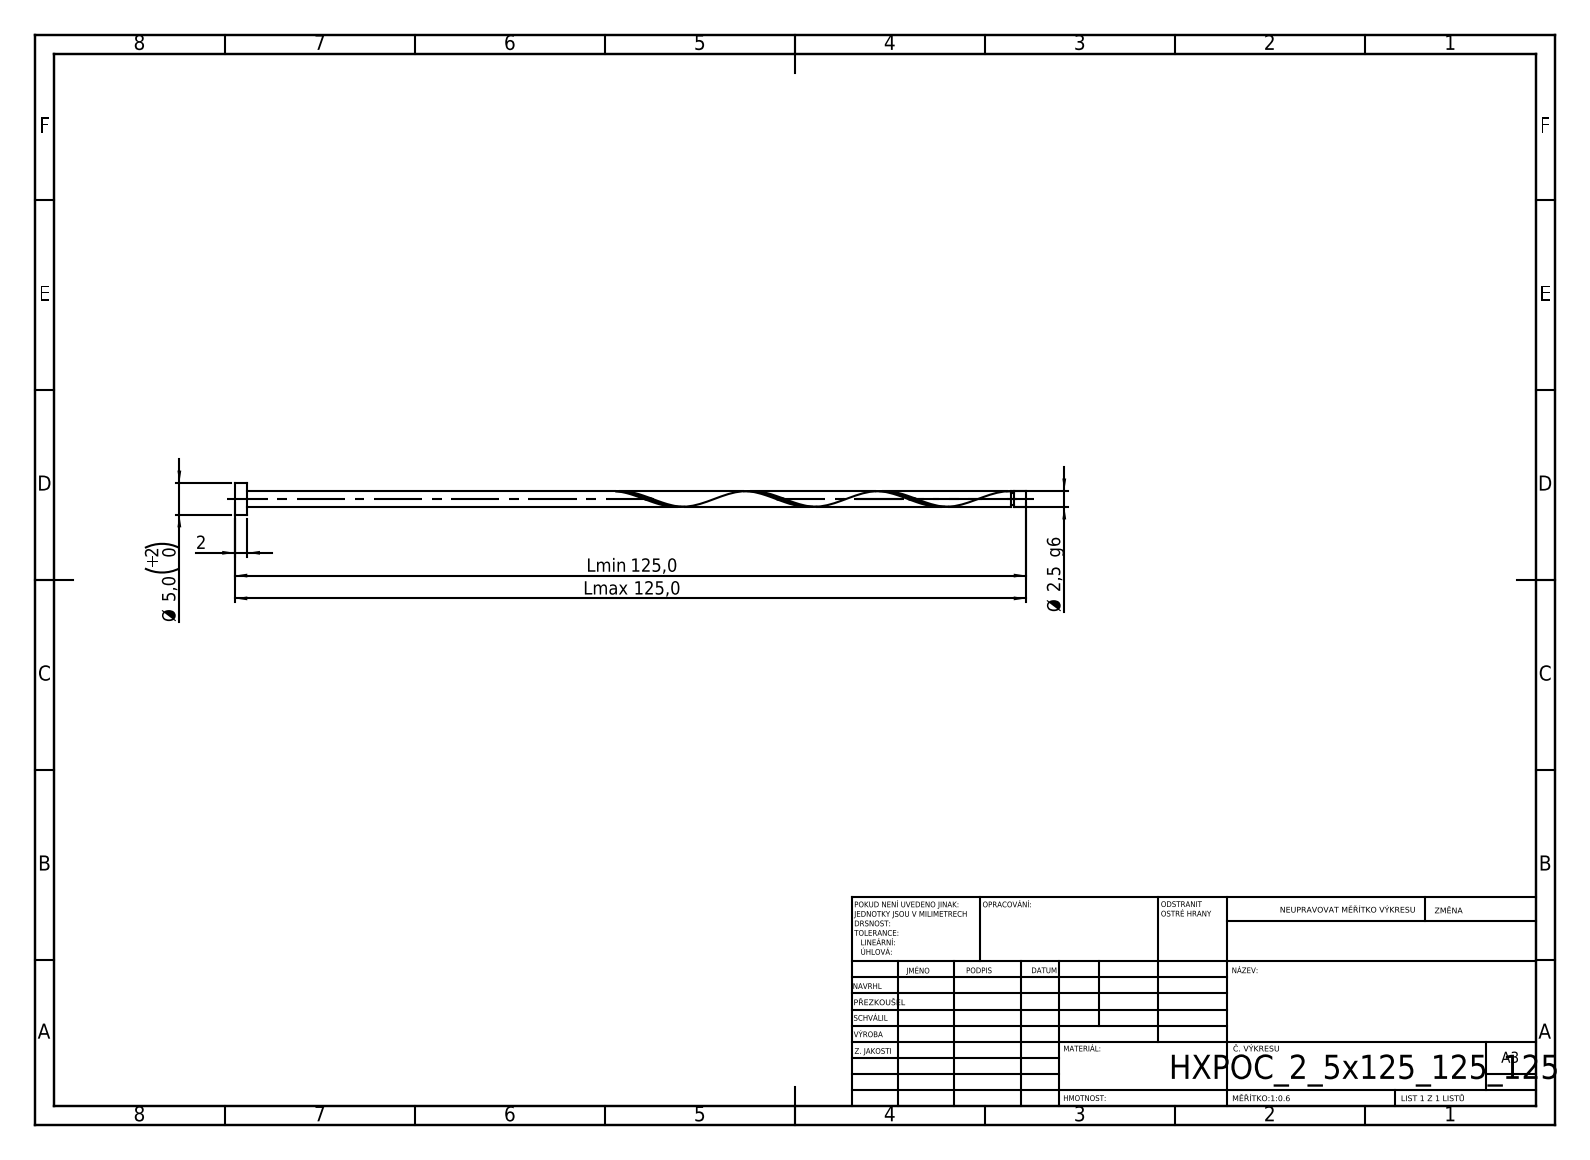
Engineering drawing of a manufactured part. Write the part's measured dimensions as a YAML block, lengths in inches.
step_written_by: "SolidWorks 2019 (CONFIG_CONTROL_DESIGN)"
units: inches
bodies: {solids: 1, faces: 21, planar: 6, cylindrical: 14, other: 1}
overall_size: [4.921, 0.197, 0.197]
volume: 0.039
surface_area: 1.637
round_bosses_or_shafts:
  - {diameter: 0.197, count: 1}
  - {diameter: 0.098, count: 1}
  - {diameter: 0.079, count: 1}
face_to_face_distances: [0.079, 4.921, 4.843, 4.846, 4.768, 0.075, 4.827, 4.748, 0.02, 0.094]
